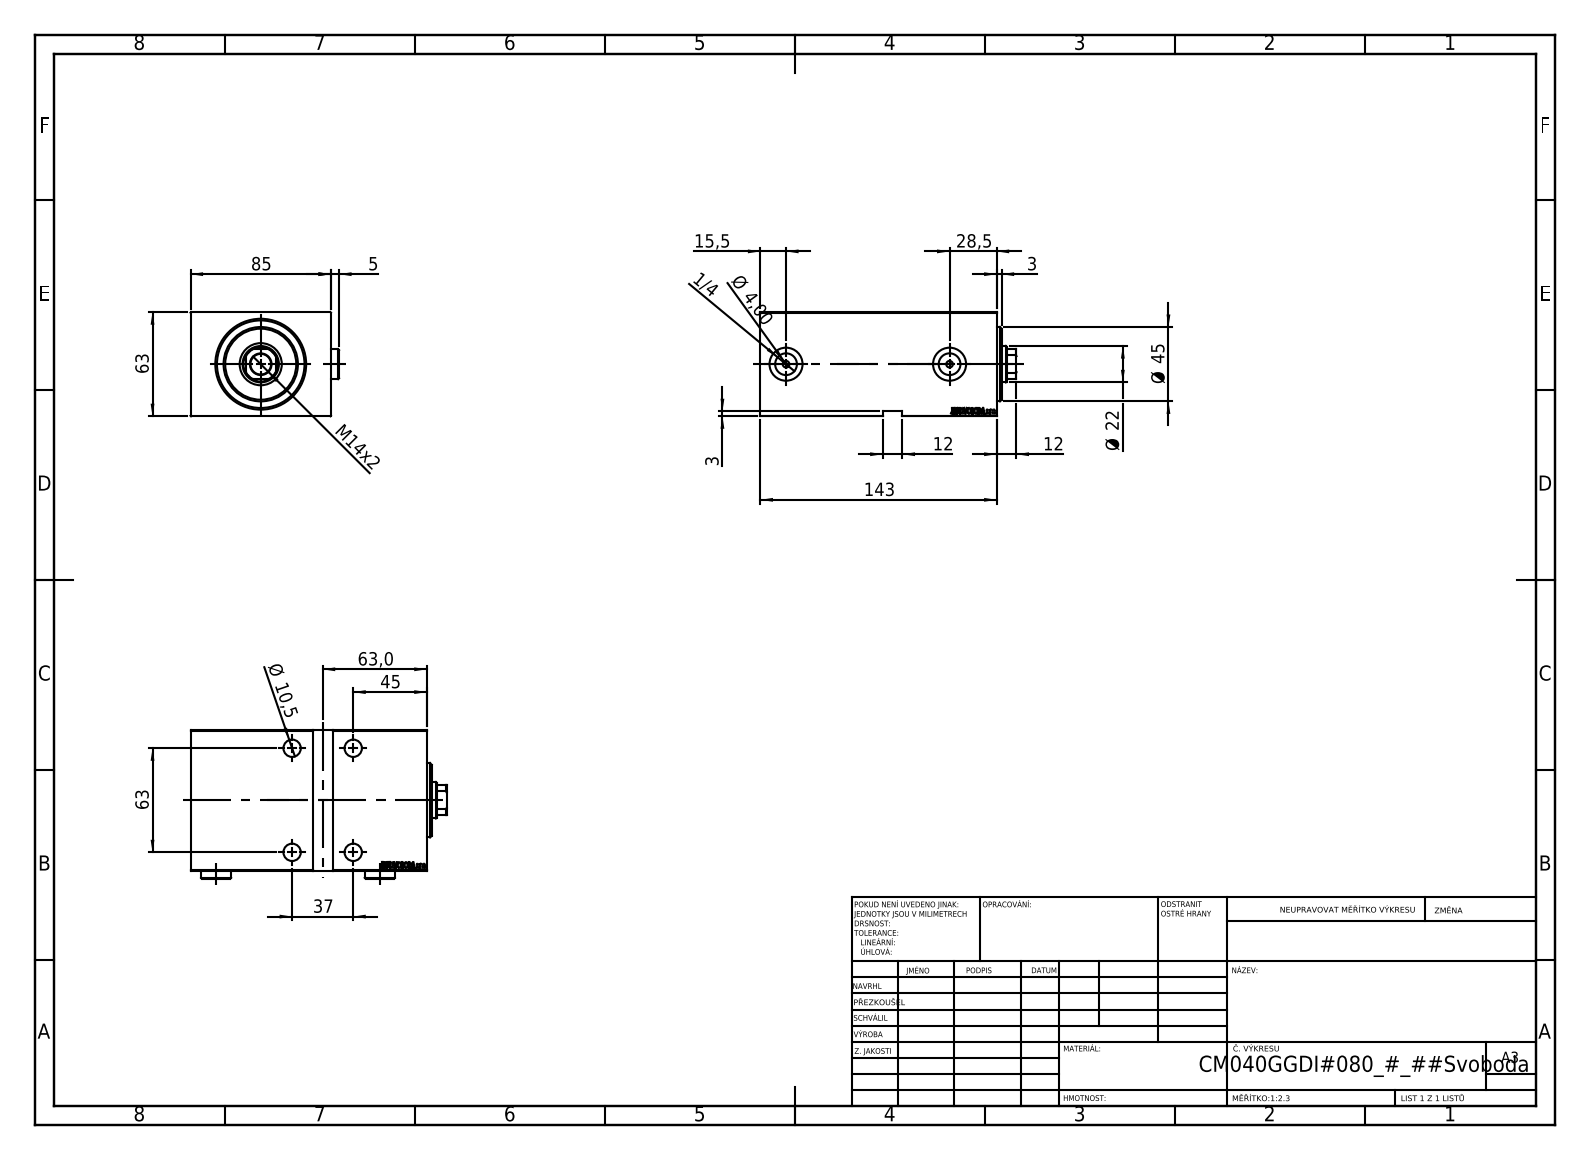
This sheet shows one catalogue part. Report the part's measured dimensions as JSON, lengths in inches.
{"part_name": "Zatka_OIL_PORT; V450CM_G_VCP; V450CM_G_Body; V450CM_VC_G", "step_written_by": "SolidWorks 2019 (CONFIG_CONTROL_DESIGN)", "units": "inches", "bodies": {"solids": 5, "faces": 915, "planar": 447, "cylindrical": 70, "other": 398}, "overall_size": [6.102, 3.539, 2.48], "volume_in3": 40.04, "surface_area_in2": 162.8, "round_holes": [[0.413, 4], [0.65, 4], [0.157, 2], [0.518, 2], [0.787, 2], [0.492, 1], [0.866, 1], [1.004, 1], [1.575, 1], [1.654, 1], [2.087, 1]], "round_bosses_or_shafts": [[0.709, 2], [1.772, 1], [1.063, 1]], "partial_cylinders_radius": [[0.413, 1]], "face_to_face_distances": [2.48, 3.346, 5.63, 0.472, 5.157, 0.197, 5.433, 4.961, 0.118, 2.362], "hole_center_spacings": [1.457, 2.48, 2.876, 3.898]}
